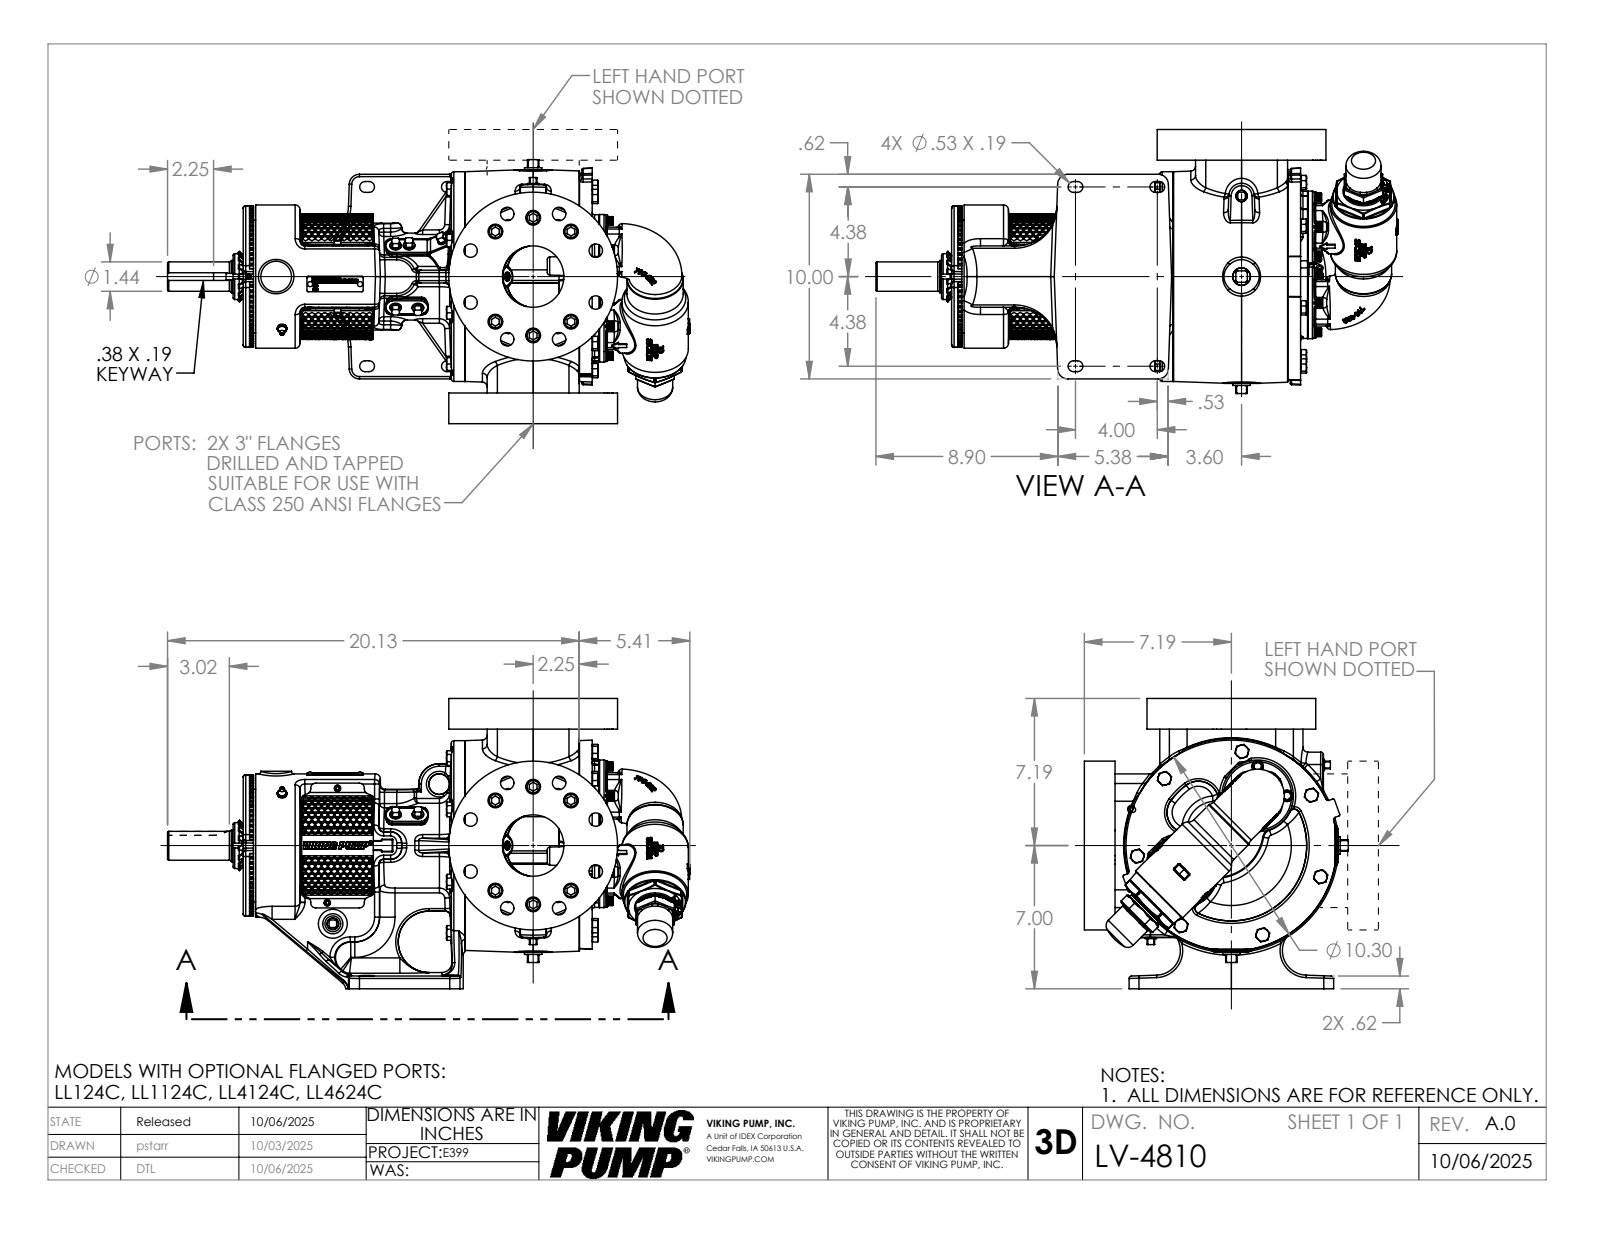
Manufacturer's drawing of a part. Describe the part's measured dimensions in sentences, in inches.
The part is named "LV-4810". Its 3-D file was written by "SolidWorks 2024 (AUTOMOTIVE_DESIGN)". It is 1 solid with 5609 faces: 1897 planar, 1174 cylindrical and 2538 other. Overall it measures 25.533 by 14.188 by 12.903 inches. Its volume is 1 100 cubic inches and its surface area 1 576 square inches. Round holes: 16 of diameter 0.656, 12 of diameter 0.719, 9 of diameter 0.25, 8 of diameter 0.368, 8 of diameter 1.094, 6 of diameter 0.199, 3 of diameter 0.159, 2 of diameter 0.266, 2 of diameter 0.313, 2 of diameter 3, 1 of diameter 0.453, 1 of diameter 1.552. Round bosses or shafts: 12 of diameter 0.66, 10 of diameter 0.625, 8 of diameter 0.563, 5 of diameter 0.625, 3 of diameter 0.312, 3 of diameter 0.19, 2 of diameter 8.25, 2 of diameter 3.5. Partial cylindrical surfaces (rounded edges, fillets, slot ends): 109 of radius 0.063, 76 of radius 0.12, 74 of radius 0.069, 48 of radius 0.24, 36 of radius 0.03, 16 of radius 0.45, 12 of radius 0.06, 12 of radius 0.25. The main face-to-face distances are 1.5, 14.187, 12.687, 14.31, 0.5, 2.25, 3.54, 10.77, 0.157, 1.343. The hole center spacings are 2.875, 3.313, 4.685, 3, 2.535, 1.375, 0.458, 0.75.
